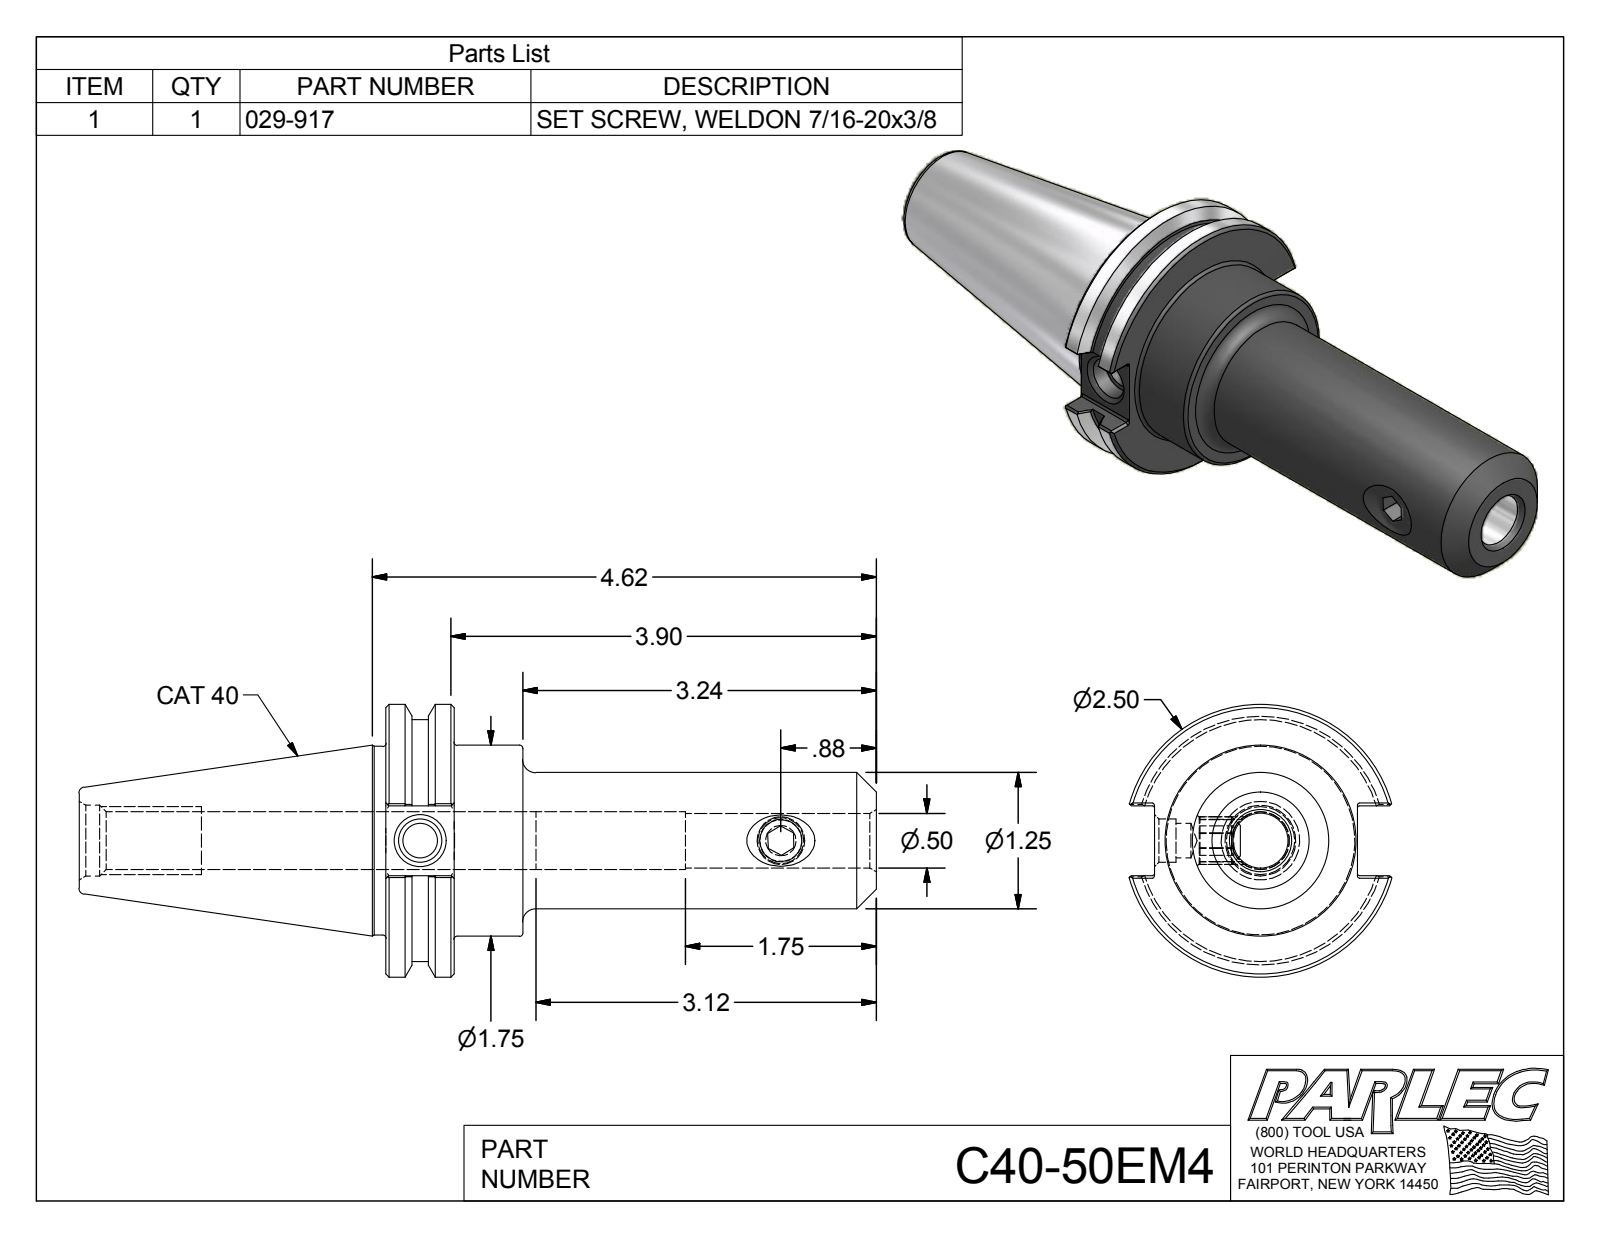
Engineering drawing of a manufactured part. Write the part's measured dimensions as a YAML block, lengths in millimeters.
part_name: "C40-50EM4; C40-50EM4-1; 029-917"
step_written_by: "Autodesk Inventor 2012 (AUTOMOTIVE_DESIGN)"
units: millimeters
bodies: {solids: 2, faces: 104, planar: 43, cylindrical: 29, other: 32}
overall_size: [185.6, 63.5, 61.1]
volume: 176200
surface_area: 34930
round_holes:
  - {diameter: 8, count: 1}
  - {diameter: 9.7, count: 1}
  - {diameter: 10.1, count: 1}
  - {diameter: 12.7, count: 1}
  - {diameter: 13.4, count: 1}
  - {diameter: 13.5, count: 1}
  - {diameter: 16.5, count: 1}
round_bosses_or_shafts:
  - {diameter: 63.5, count: 1}
  - {diameter: 56.4, count: 1}
  - {diameter: 44.5, count: 1}
  - {diameter: 43.9, count: 1}
  - {diameter: 31.8, count: 1}
  - {diameter: 11.1, count: 1}
partial_cylinders:
  - {radius: 0.5, count: 12}
face_to_face_distances: [15.9, 31.9, 16, 114.2, 98.3, 82.3, 16.3, 47.2, 71.4, 87.3]
hole_center_spacings: [83.9]
